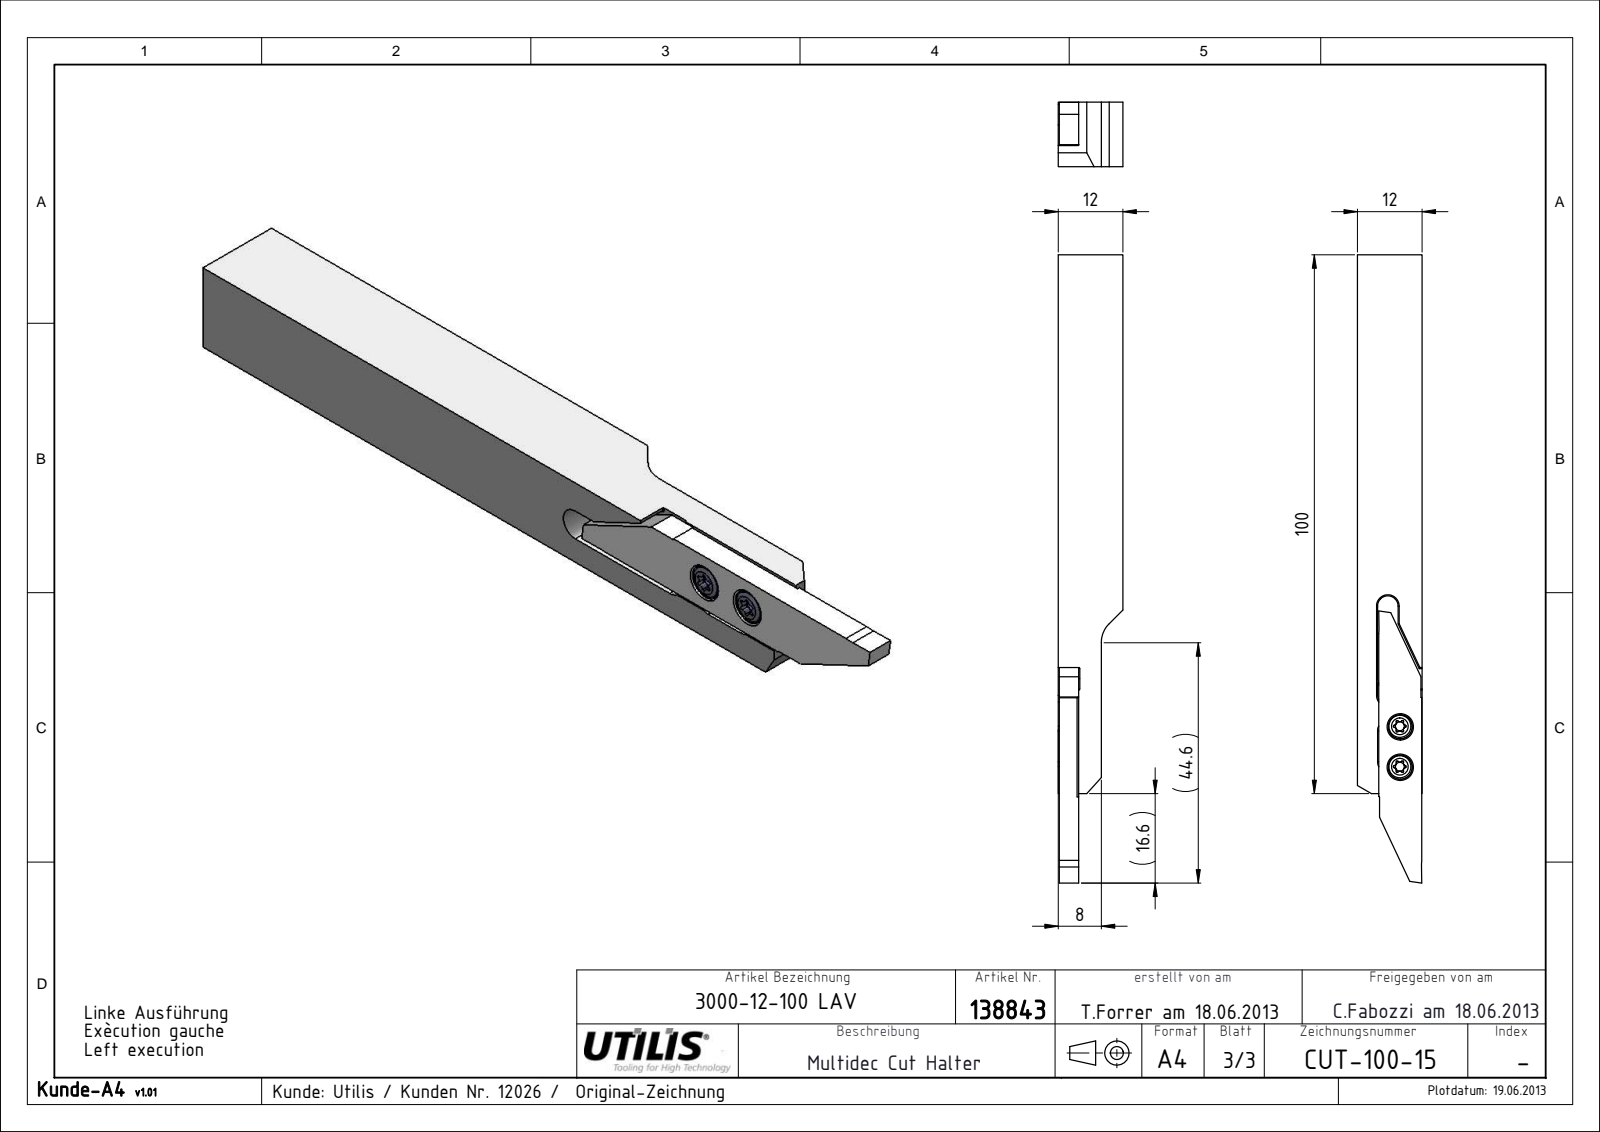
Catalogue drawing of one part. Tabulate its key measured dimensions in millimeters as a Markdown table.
| quantity | value |
| --- | --- |
| part name | CUT-100-15 |
| STEP written by | SolidWorks 2016 (AUTOMOTIVE_DESIGN) |
| units | millimeters |
| bodies | 1 solid, 45 faces (33 planar, 8 cylindrical, 4 other) |
| overall size | 116.6 × 12 × 12 |
| volume | 12 997 mm³ |
| surface area | 5 361 mm² |
| partial cylindrical surfaces (radius × count) | 2.1 × 4, 10 × 2, 5 × 1 |
| main face-to-face distances | 12, 8, 4, 11.8, 7.8, 4.2, 8.2, 3.8, 3.6, 11.95 |
